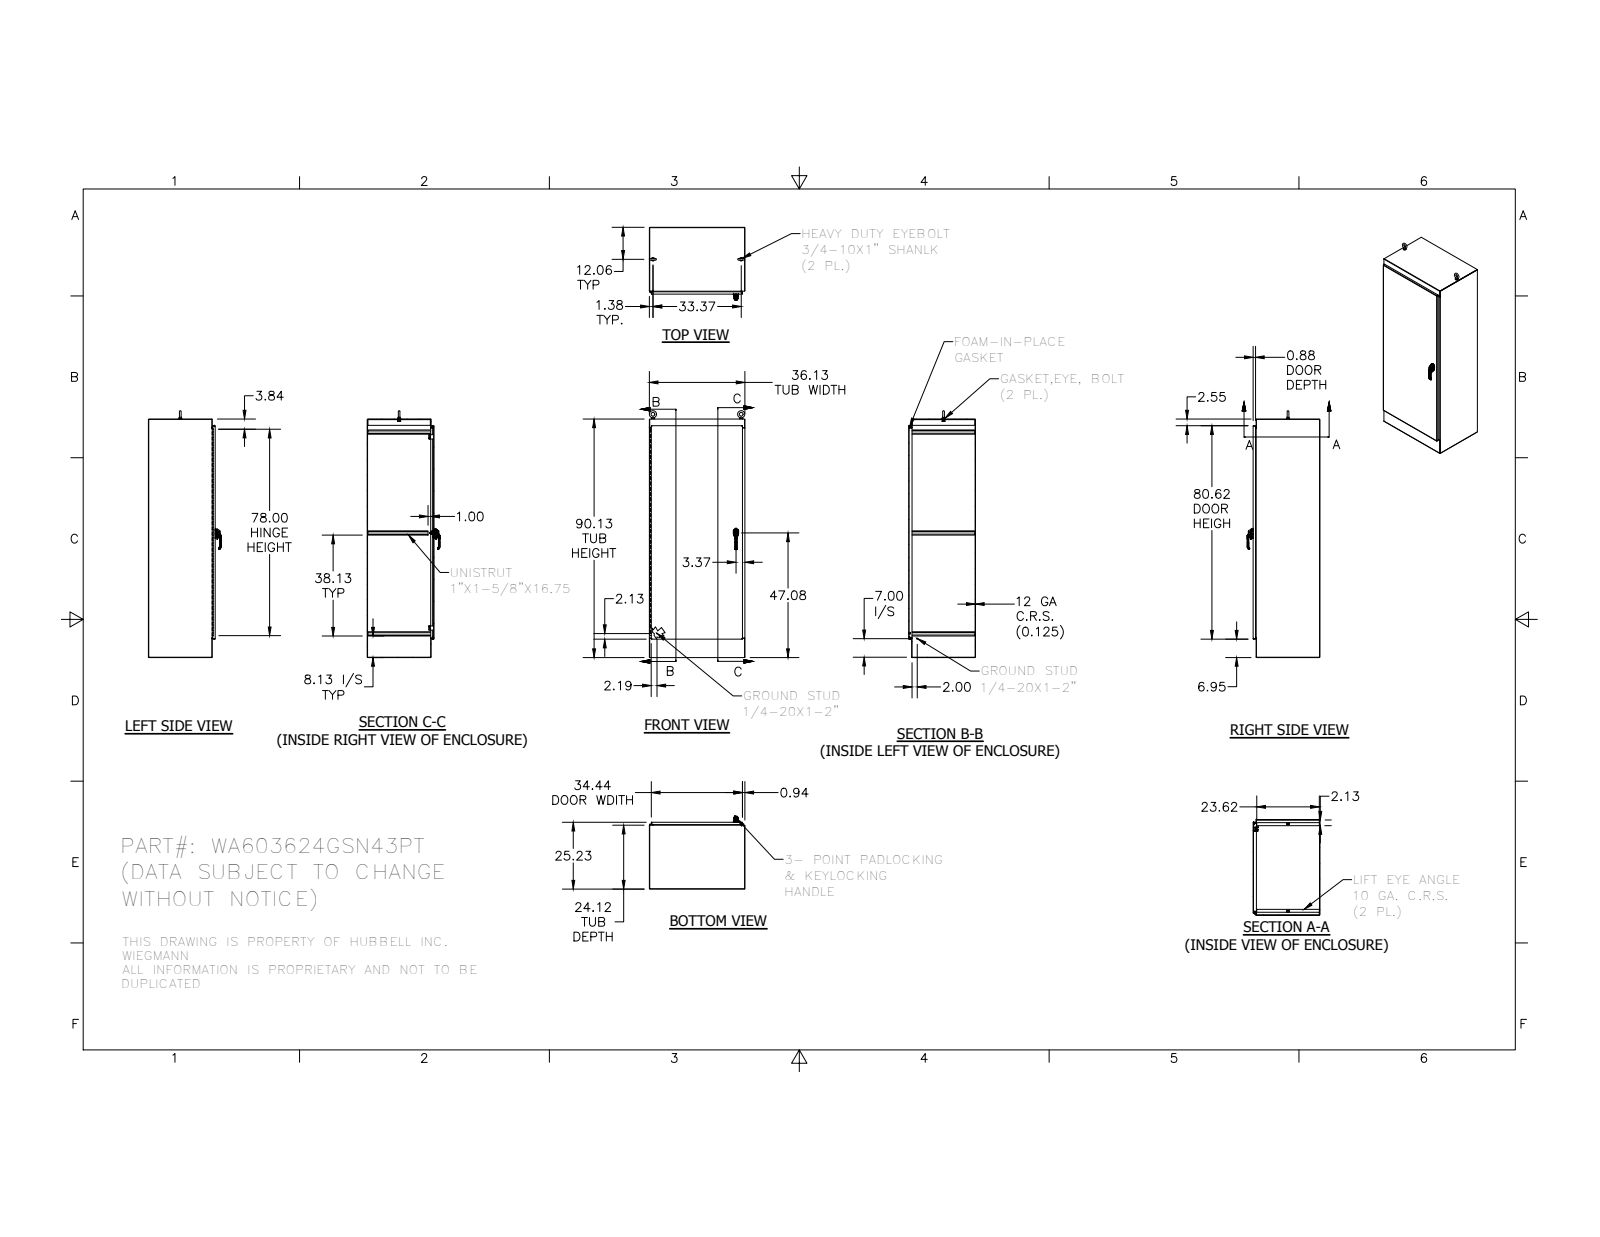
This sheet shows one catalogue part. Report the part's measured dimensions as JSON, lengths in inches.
{"part_name": "WA9036FSN43PTFB; WA9036FSN43PTDR; HFW3762; 1091-903_AF0_1 (+8 more)", "step_written_by": "SolidWorks 2014 (AUTOMOTIVE_DESIGN)", "units": "inches", "bodies": {"solids": 52, "faces": 1844, "planar": 833, "cylindrical": 691, "other": 320}, "overall_size": [93.248, 36.125, 25.23], "volume_in3": 1794, "surface_area_in2": 28991, "round_holes": [[0.277, 8], [0.375, 8], [0.2, 4], [0.28, 3], [0.241, 2], [0.25, 2], [0.252, 2], [0.4, 2], [0.407, 2], [0.45, 2], [0.642, 2], [0.813, 2]], "round_bosses_or_shafts": [[1.25, 2], [1.12, 2], [1, 2], [0.75, 2], [0.563, 2], [0.527, 2], [0.5, 2], [0.375, 2]], "partial_cylinders_radius": [[0.01, 16], [0.125, 16], [0.031, 15], [0.156, 15], [0.05, 14], [0.019, 12], [0.053, 12], [0.086, 12]], "face_to_face_distances": [0.125, 36, 0.125, 24.98, 25.105, 25.23, 25.104, 35.875, 36.125, 90], "hole_center_spacings": [8.667, 26, 17.333, 34.667, 71.883, 72.633, 0.762, 0.764]}
